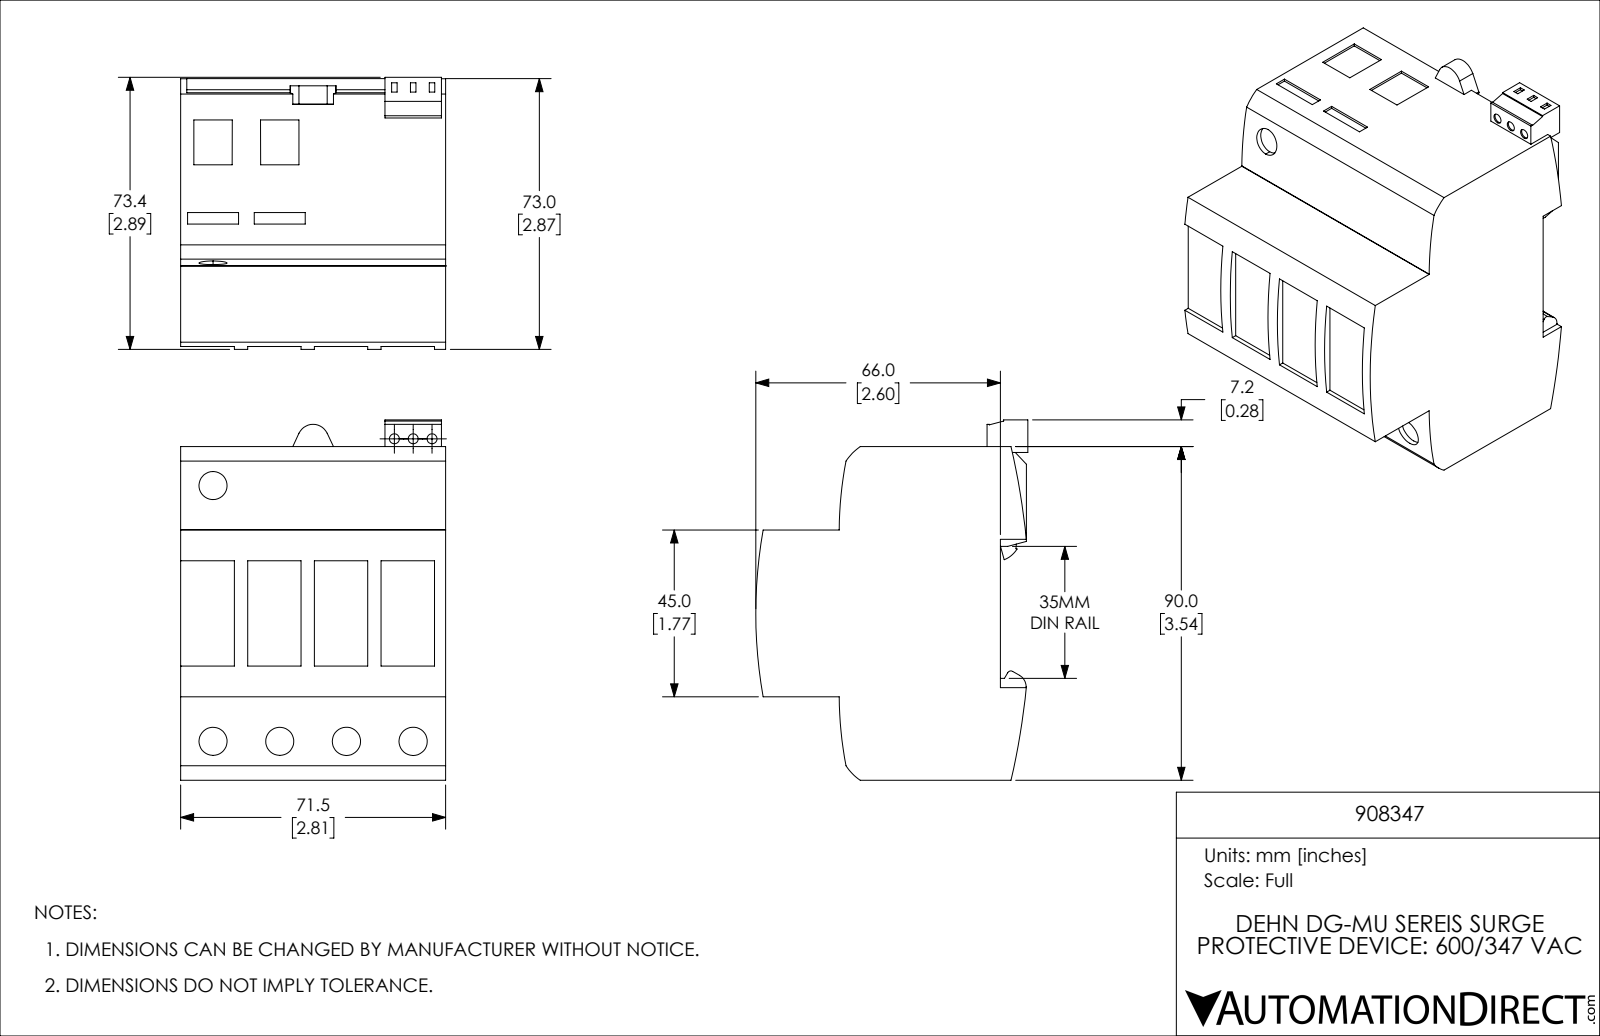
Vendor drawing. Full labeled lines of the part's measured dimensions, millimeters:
Part name (STEP PRODUCT): 908347
STEP written by: SolidWorks 2019 (CONFIG_CONTROL_DESIGN)
Units: millimetres
Bodies: 1 solid, 178 faces (142 planar, 25 cylindrical, 11 other)
Overall size (bounding box): 97.2 × 73.4 × 71.5
Volume: 367 400 mm³ · Surface area: 35 050 mm²
Round holes (diameter × count): ⌀2.7 ×3
Partial cylindrical surfaces — rounded edges, fillets, slot ends (radius × count): R2 ×2, R100 ×2, R1 ×1, R3.5 ×1, R4.2 ×1, R14 ×1, R14 ×1, R98.5 ×1
Main face-to-face distances: 71.5, 22.5, 67.5, 90, 64, 45, 7, 71, 66.9, 0.7
Hole centre spacings: 5.1, 5.1, 10.2
